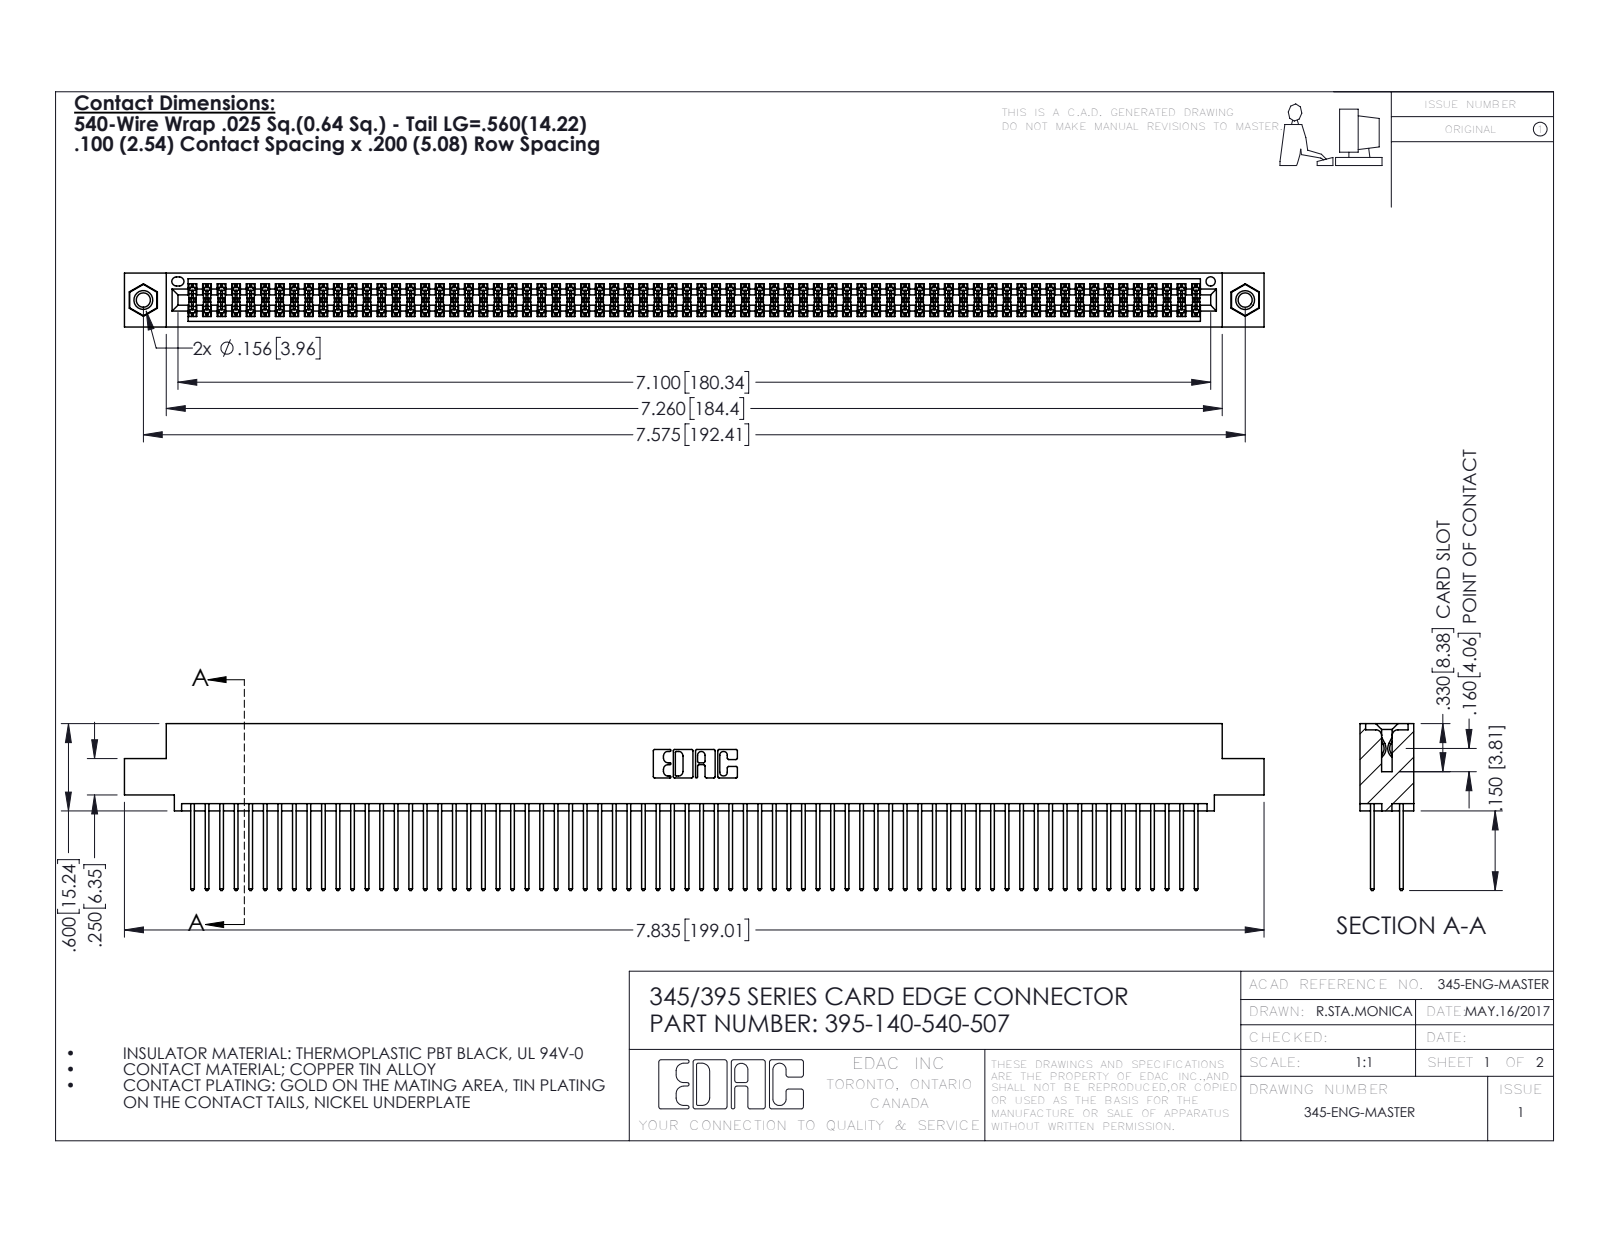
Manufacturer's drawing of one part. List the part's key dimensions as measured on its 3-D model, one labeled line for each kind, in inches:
Part name (STEP PRODUCT): 395-140-540-507; 345-250-001_345-250-005-103; 345-292-001_345-293-140; 345 Part_0.110 Offset - 0.156 Dia-TI
STEP written by: SolidWorks 2016 (CONFIG_CONTROL_DESIGN)
Units: inches
Bodies: 143 solids, 7190 faces (4736 planar, 2438 cylindrical, 16 other)
Overall size (bounding box): 7.835 × 1.147 × 0.37
Volume: 1.223 in³ · Surface area: 50.75 in²
Round holes (diameter × count): ⌀0.098 ×2, ⌀0.125 ×2, ⌀0.156 ×2, ⌀0.064 ×1
Round bosses / shafts (diameter × count): ⌀0.155 ×2
Partial cylindrical surfaces — rounded edges, fillets, slot ends (radius × count): R0.006 ×210, R0.01 ×140, R0.01 ×22, R0.007 ×6, R0.031 ×6, R0.026 ×3, R0.014 ×2, R0.019 ×2
Main face-to-face distances: 0.072, 0.298, 0.2, 0.098, 0.272, 0.025, 0.225, 0.37, 0.175, 0.149
Hole centre spacings: 0.27, 7.339, 7.575
